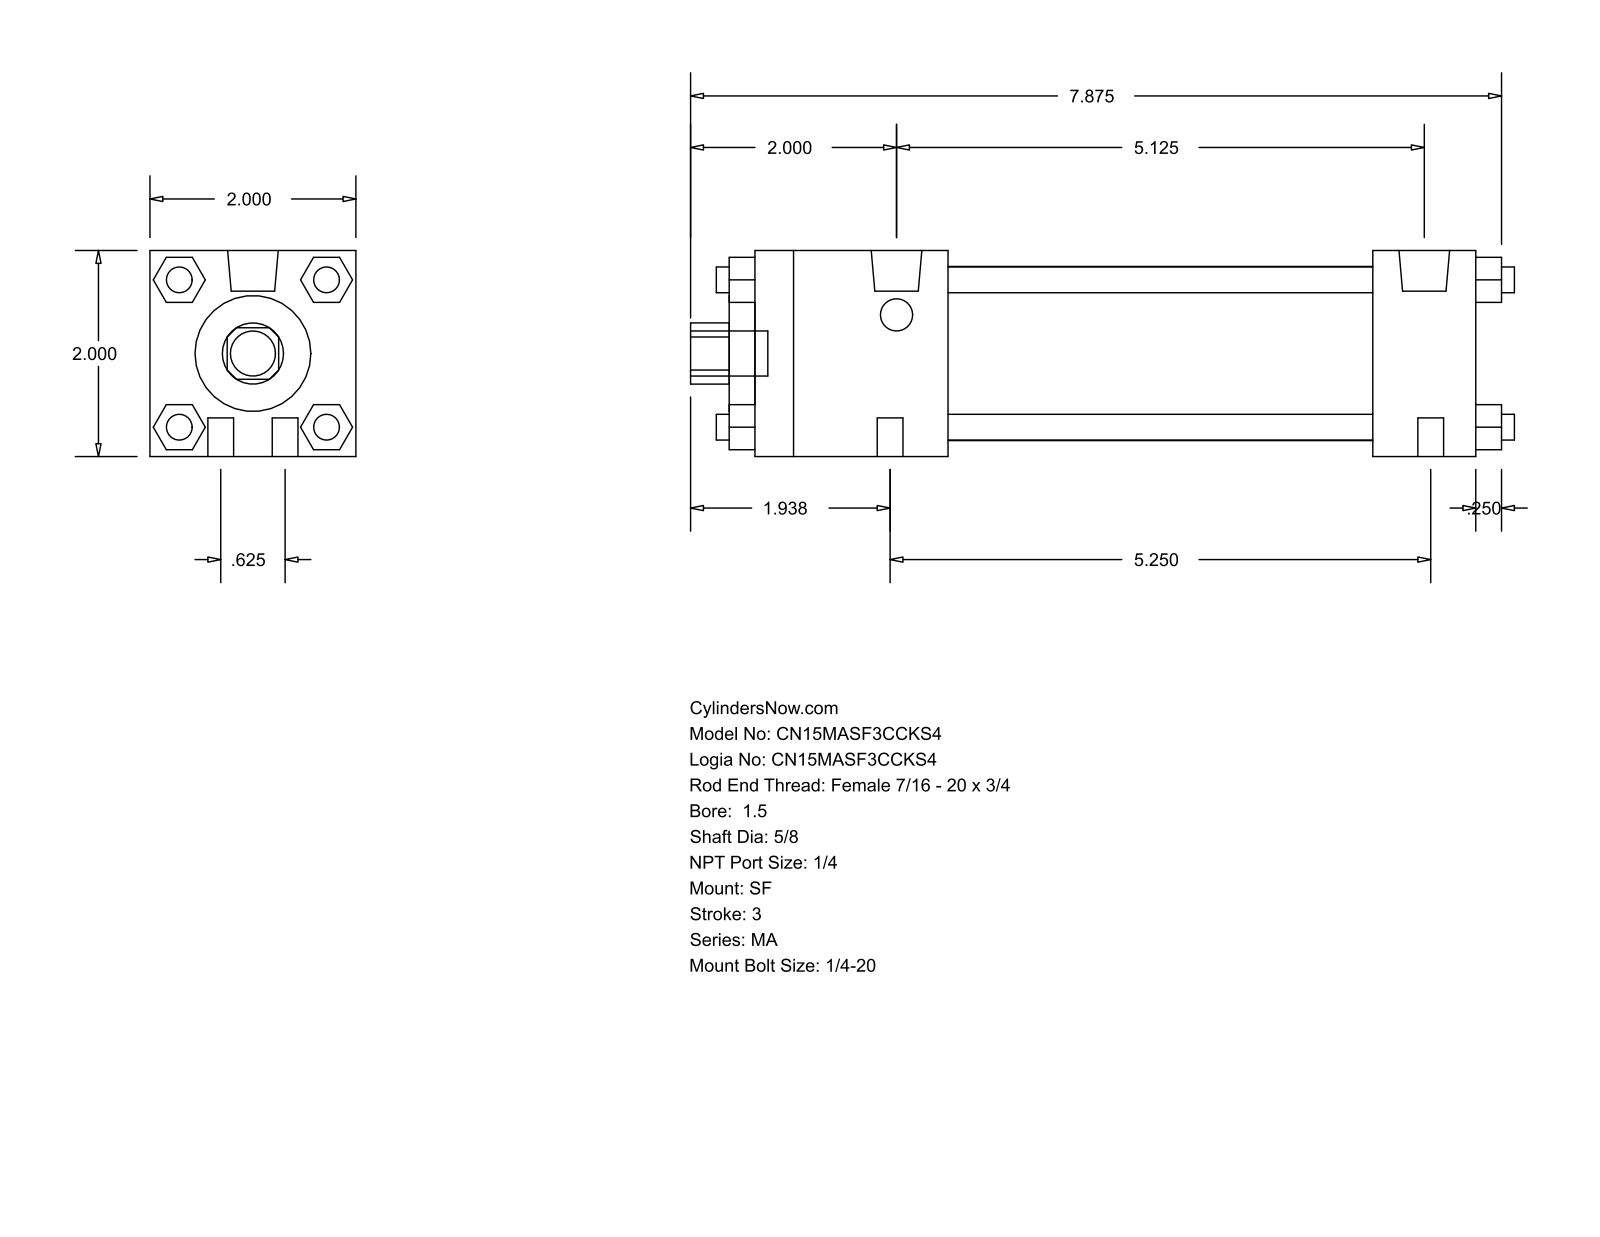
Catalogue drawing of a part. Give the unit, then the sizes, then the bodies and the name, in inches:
Units: inches
Overall size (bounding box): 8 × 2 × 2
Round holes (diameter × count): ⌀0.625 ×1, ⌀1.125 ×1, ⌀1.69 ×1
Round bosses / shafts (diameter × count): ⌀0.25 ×8, ⌀0.492 ×2, ⌀0.313 ×2, ⌀0.437 ×1
Partial cylindrical surfaces — rounded edges, fillets, slot ends (radius × count): R0.297 ×1
Main face-to-face distances: 2, 7, 0.25, 7.25, 1.875, 6, 4.125, 5.125, 1, 2.125
Bodies: 0 solids, 124 faces (94 planar, 30 cylindrical, 0 other)
Part name (STEP PRODUCT): MA_SF__0150_0.625
STEP written by: GSSL Pune (CONFIG_CONTROL_DESIGN)
